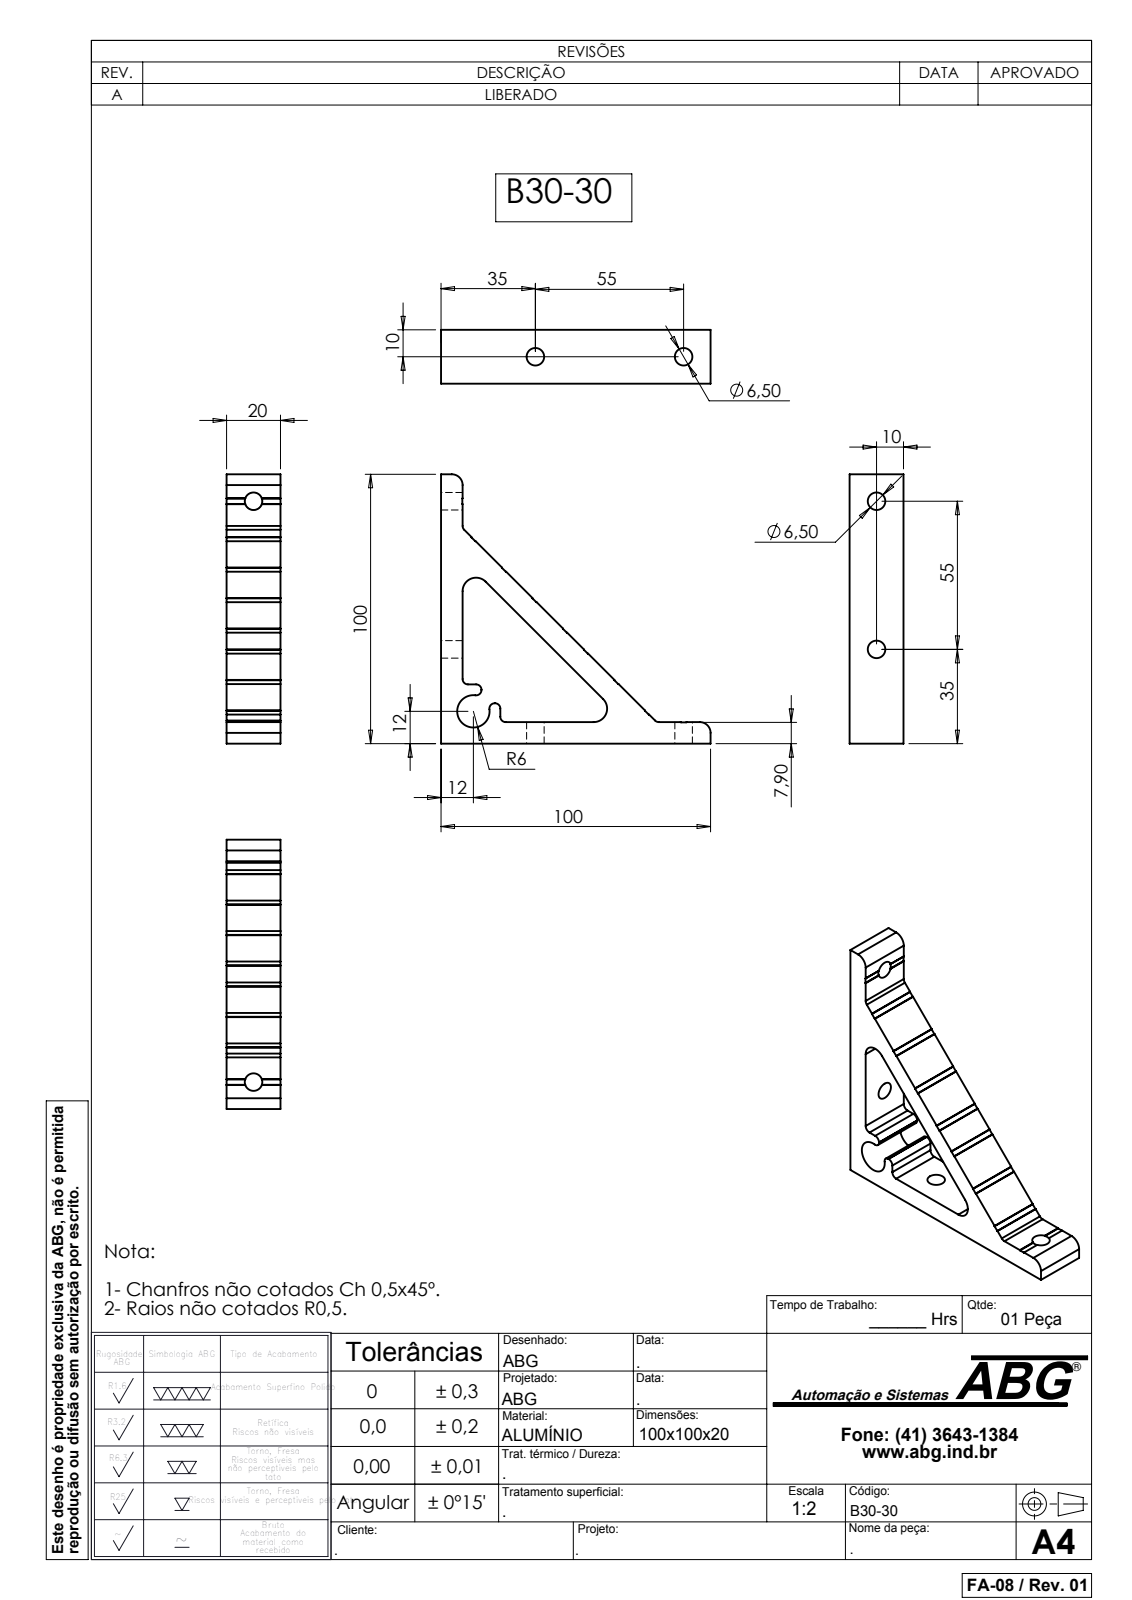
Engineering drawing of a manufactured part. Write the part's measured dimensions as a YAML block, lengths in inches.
part_name: "B30-30"
step_written_by: "SolidWorks 2007 (CONFIG_CONTROL_DESIGN)"
units: inches
bodies: {solids: 1, faces: 82, planar: 58, cylindrical: 24, other: 0}
overall_size: [3.937, 3.937, 0.787]
volume: 2.832
surface_area: 25.34
round_holes:
  - {diameter: 0.256, count: 4}
partial_cylinders:
  - {radius: 0.079, count: 8}
  - {radius: 0.157, count: 2}
  - {radius: 0.197, count: 2}
  - {radius: 0.236, count: 1}
face_to_face_distances: [0.315, 0.787, 0.311, 3.937, 3.622, 0.866, 0.551, 3.071, 0.555, 3.626]
hole_center_spacings: [2.165]
